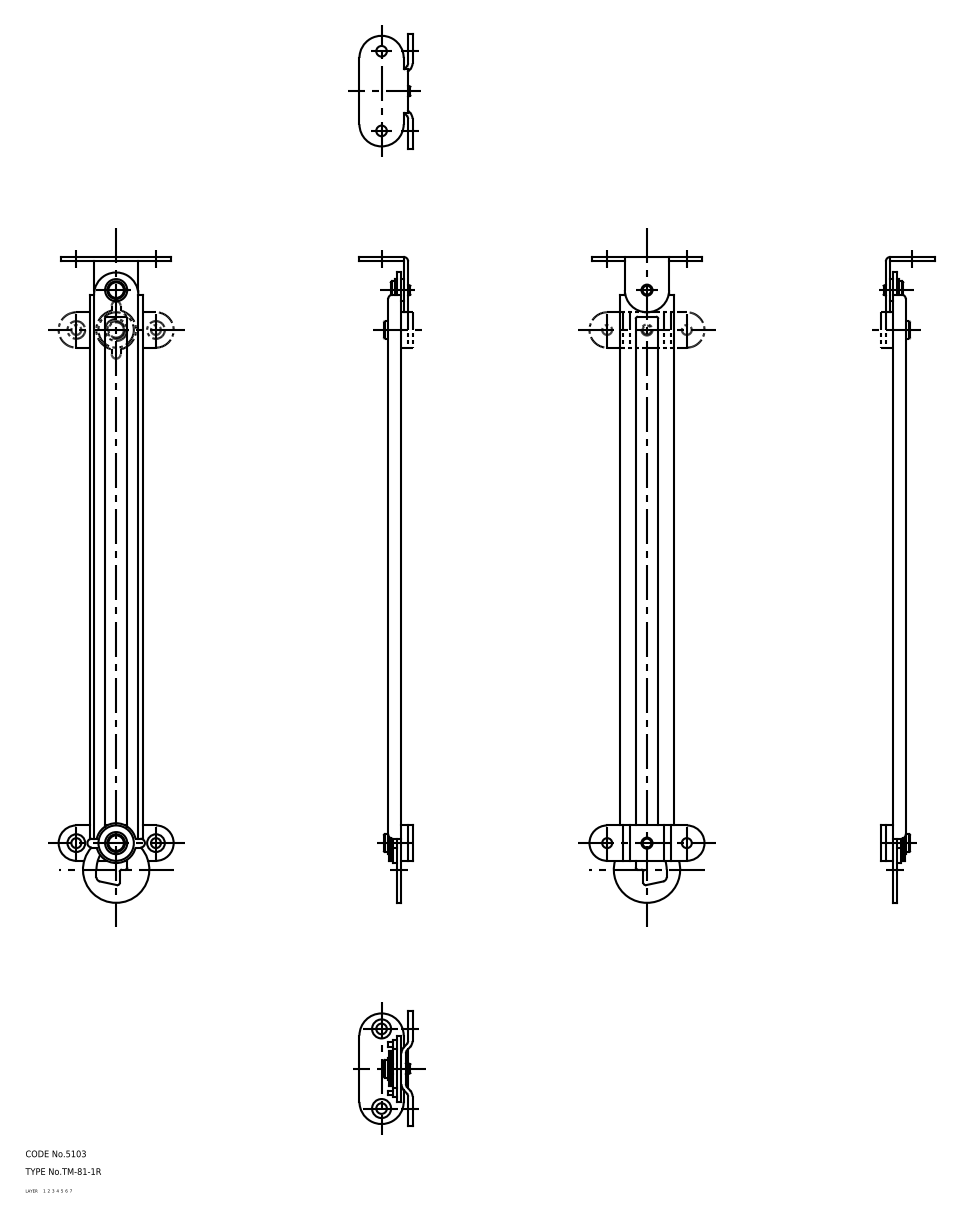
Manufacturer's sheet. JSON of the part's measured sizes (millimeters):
{"part_name": "67118247; 67118260; 67118273; 67118286 (+7 more)", "step_written_by": "CADfix (AUTOMOTIVE_DESIGN)", "units": "millimeters", "bodies": {"solids": 11, "faces": 162, "planar": 0, "cylindrical": 0, "other": 162}, "overall_size": [292, 52, 24], "volume_mm3": 17020, "surface_area_mm2": 21316}
